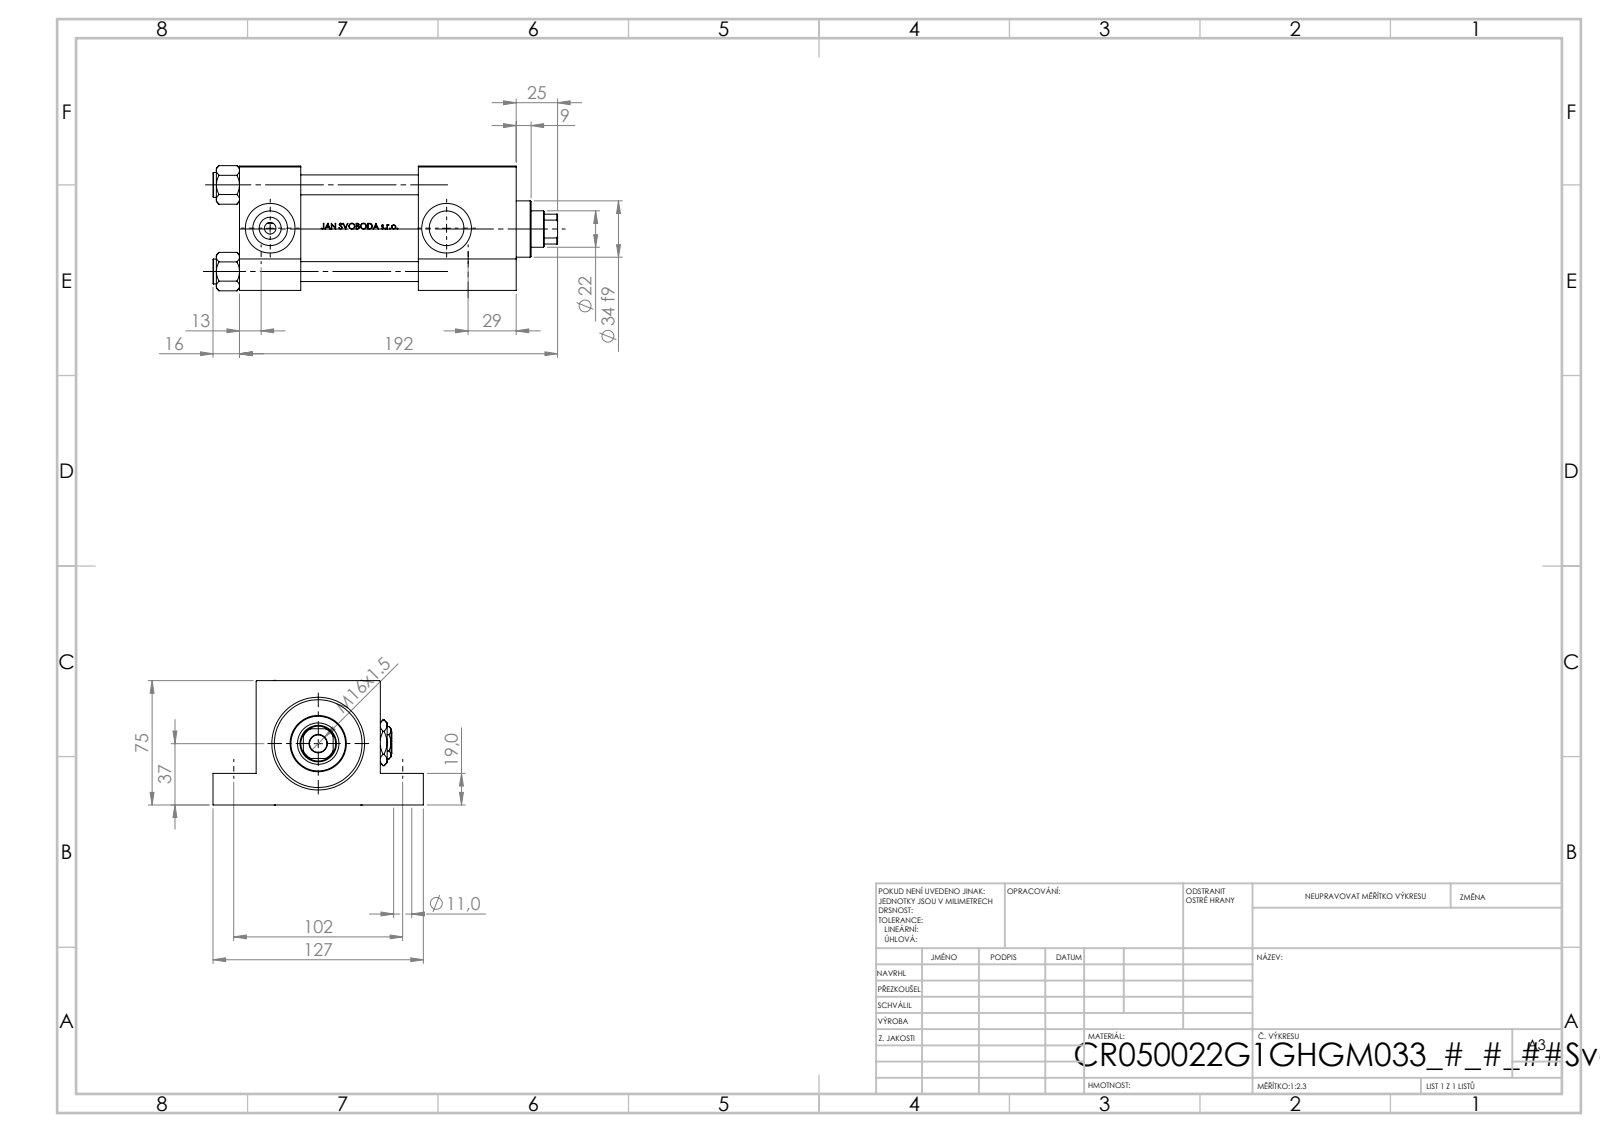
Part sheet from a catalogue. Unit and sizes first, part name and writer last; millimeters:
Units: millimetres
Overall size (bounding box): 208 × 127 × 75.54
Round holes (diameter × count): ⌀11 ×4, ⌀12 ×4, ⌀7 ×2, ⌀20.96 ×2, ⌀30 ×2, ⌀10.5 ×1, ⌀22 ×1, ⌀25 ×1, ⌀41 ×1, ⌀50 ×1, ⌀53 ×1
Round bosses / shafts (diameter × count): ⌀15 ×4, ⌀56 ×1, ⌀34 ×1
Partial cylindrical surfaces — rounded edges, fillets, slot ends (radius × count): R10.5 ×1
Main face-to-face distances: 75, 37, 167, 130, 19, 56, 71, 108, 59, 101
Hole centre spacings: 52.3, 36.63, 37.34, 73.96, 102, 125, 161.34, 106.5
Volume: 769 720 mm³ · Surface area: 168 492 mm²
Bodies: 12 solids, 1134 faces (454 planar, 128 cylindrical, 552 other)
Part name (STEP PRODUCT): V215CR_VCP_G; V215_VC_A; Zatka_pro_OIL_PORT; NUT_M5_G (+2 more)
STEP written by: SolidWorks 2019 (CONFIG_CONTROL_DESIGN)
